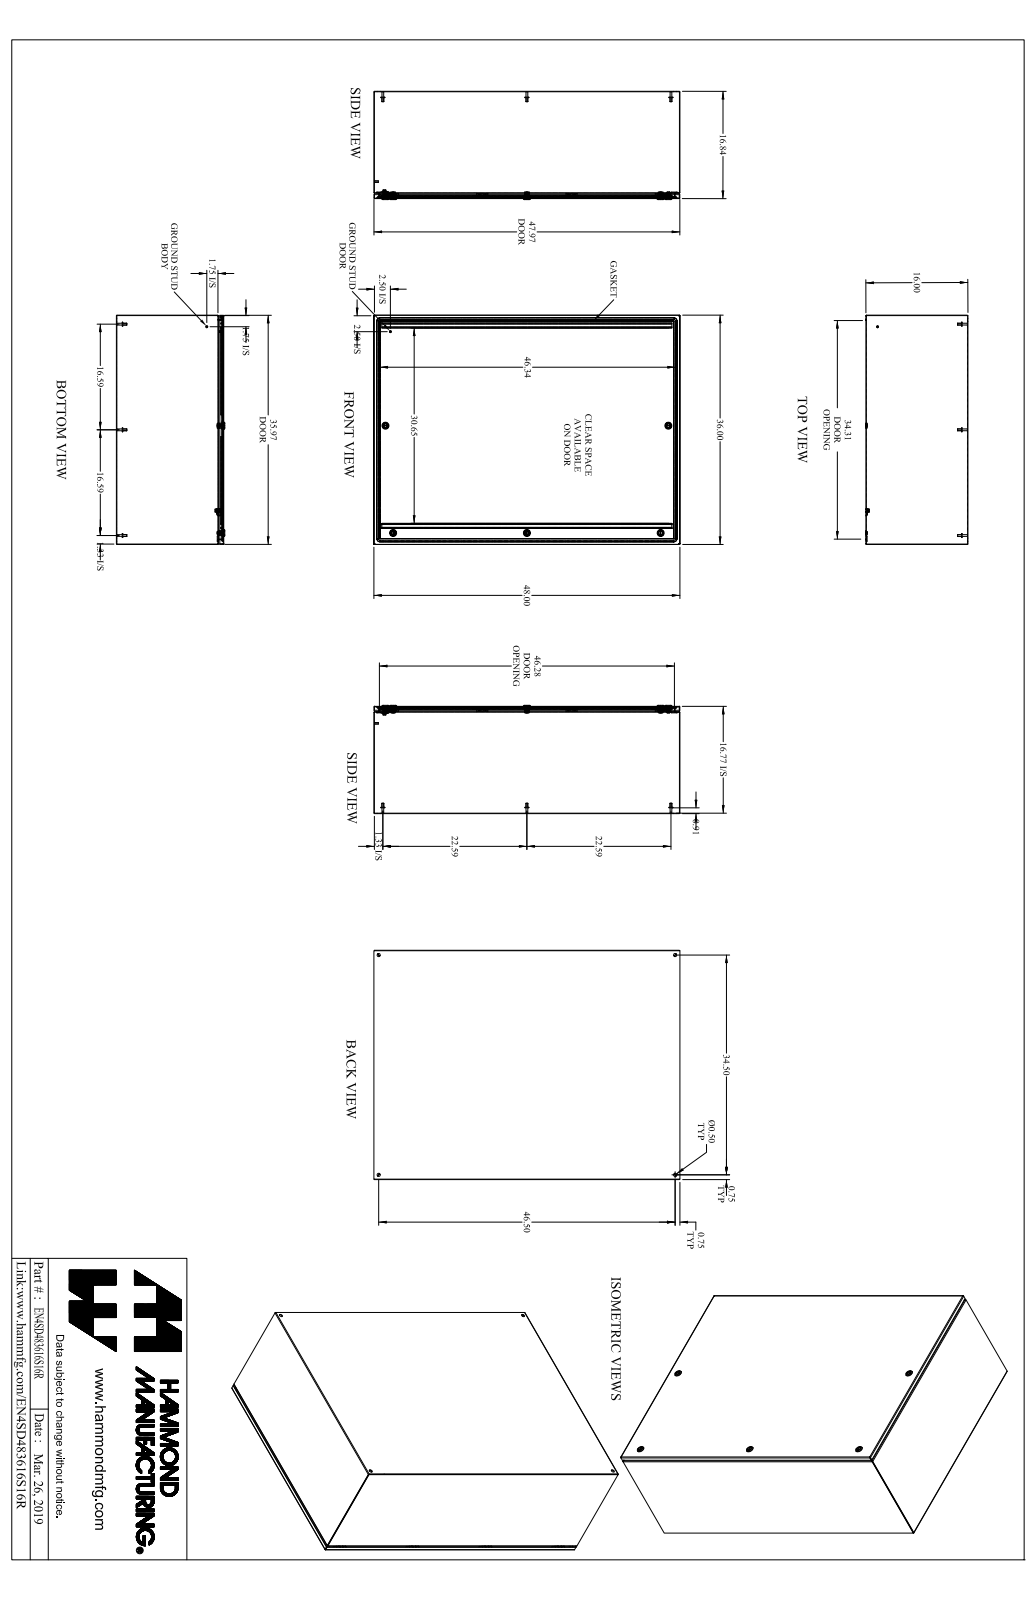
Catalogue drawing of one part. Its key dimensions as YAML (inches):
part_name: "EN4SD483616S16R"
step_written_by: "SolidWorks 2018 (AUTOMOTIVE_DESIGN)"
units: inches
bodies: {solids: 66, faces: 1714, planar: 896, cylindrical: 545, other: 273}
overall_size: [48, 36, 17.002]
volume: 496.6
surface_area: 13983
round_holes:
  - {diameter: 0.5, count: 9}
  - {diameter: 0.197, count: 5}
  - {diameter: 0.387, count: 5}
  - {diameter: 0.63, count: 5}
  - {diameter: 0.768, count: 5}
  - {diameter: 0.172, count: 2}
  - {diameter: 0.196, count: 1}
  - {diameter: 0.24, count: 1}
  - {diameter: 0.242, count: 1}
  - {diameter: 0.275, count: 1}
  - {diameter: 0.375, count: 1}
round_bosses_or_shafts:
  - {diameter: 0.625, count: 11}
  - {diameter: 0.313, count: 10}
  - {diameter: 0.275, count: 8}
  - {diameter: 1.1, count: 5}
  - {diameter: 0.236, count: 5}
  - {diameter: 0.785, count: 3}
  - {diameter: 0.625, count: 3}
  - {diameter: 0.525, count: 3}
partial_cylinders:
  - {radius: 0.048, count: 32}
  - {radius: 0.01, count: 24}
  - {radius: 0.036, count: 18}
  - {radius: 0.108, count: 18}
  - {radius: 0.062, count: 17}
  - {radius: 0.094, count: 10}
  - {radius: 0.125, count: 10}
  - {radius: 0.016, count: 9}
face_to_face_distances: [0.072, 16.77, 16.698, 16.842, 35.928, 35.856, 36, 0.072, 47.856, 47.928]
hole_center_spacings: [16.634, 16.881, 17.931, 23.274, 27.854, 33.516, 34.5, 40.728]
